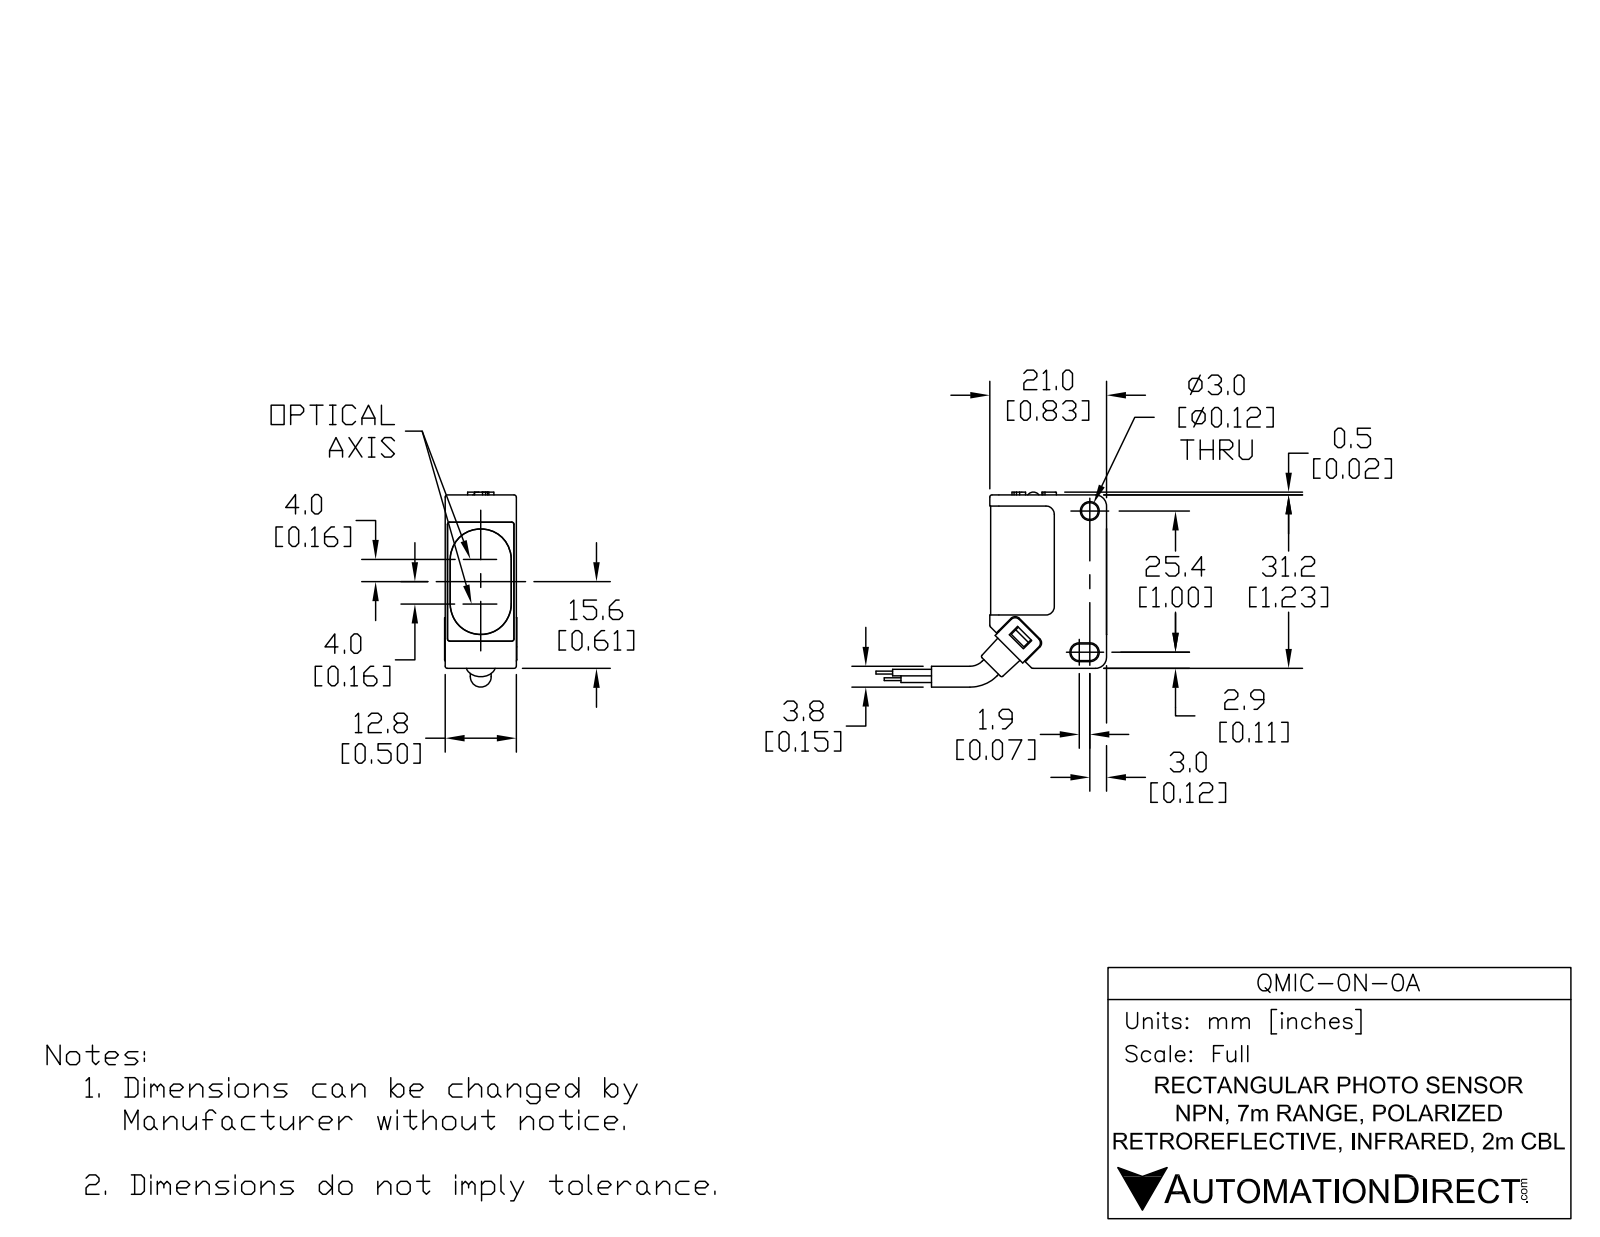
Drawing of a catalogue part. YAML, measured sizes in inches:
part_name: "QMIC-0N-0A"
step_written_by: "SolidWorks 2017 (AUTOMOTIVE_DESIGN)"
units: inches
bodies: {solids: 9, faces: 258, planar: 134, cylindrical: 100, other: 24}
overall_size: [3.193, 1.032, 0.512]
volume: 0.47
surface_area: 8.375
round_holes:
  - {diameter: 0.118, count: 3}
  - {diameter: 0.148, count: 1}
  - {diameter: 0.224, count: 1}
  - {diameter: 0.283, count: 1}
round_bosses_or_shafts:
  - {diameter: 0.138, count: 2}
partial_cylinders:
  - {radius: 0.016, count: 13}
  - {radius: 0.02, count: 10}
  - {radius: 0.039, count: 8}
  - {radius: 0.059, count: 6}
  - {radius: 0.024, count: 4}
  - {radius: 0.006, count: 2}
  - {radius: 0.035, count: 2}
  - {radius: 0.044, count: 2}
face_to_face_distances: [0.02, 0.498, 0.059, 0.016, 0.504, 0.138, 0.488, 0.079, 0.482, 0.492]
hole_center_spacings: [0.205]
